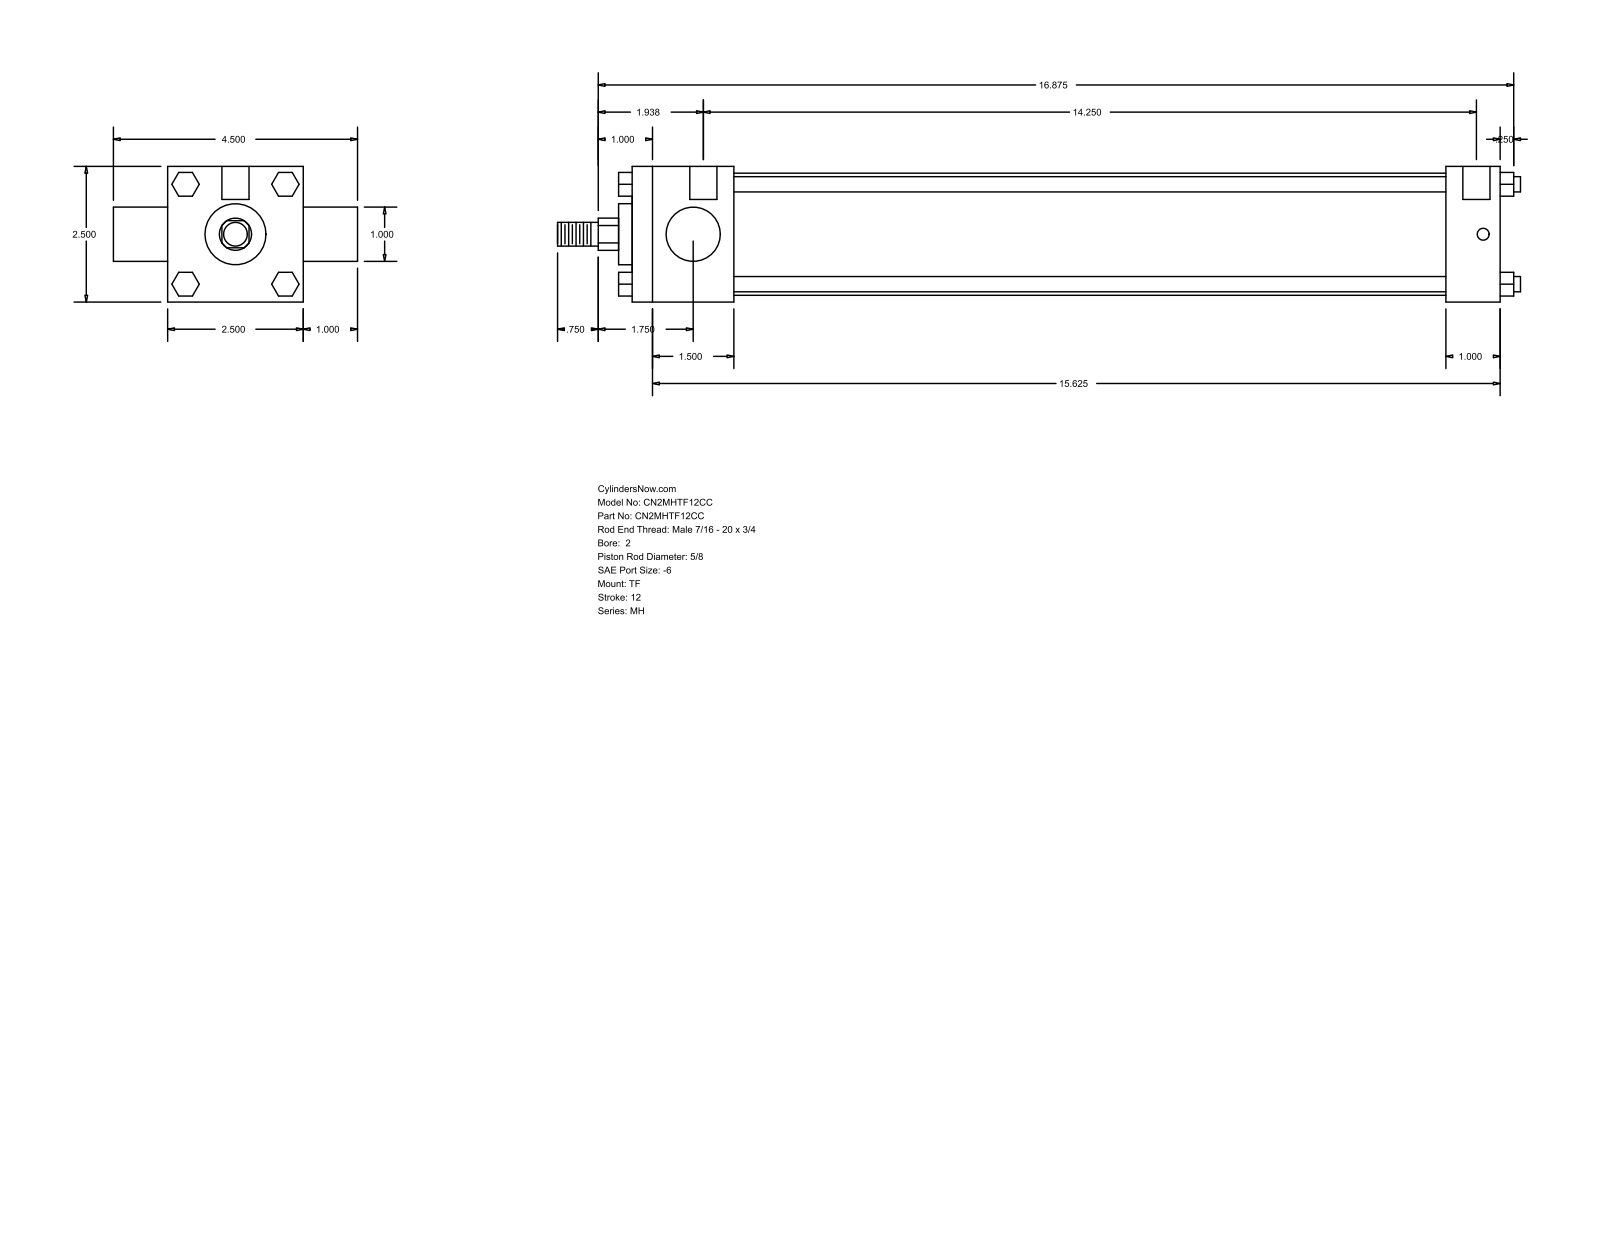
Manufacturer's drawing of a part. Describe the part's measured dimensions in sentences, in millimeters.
The part is named "MH_TF__0200_0.625". Its 3-D file was written by "GSSL Pune (CONFIG_CONTROL_DESIGN)". It is 0 solids with 120 faces: 92 planar, 28 cylindrical and 0 other. Overall it measures 450.85 by 114.3 by 63.5 millimeters. Round holes: 3 of diameter 5.56, 2 of diameter 12.7. Round bosses or shafts: 4 of diameter 7.14, 1 of diameter 57.15, 1 of diameter 28.57, 1 of diameter 25.4, 1 of diameter 15.88, 1 of diameter 11.11. Partial cylindrical surfaces (rounded edges, fillets, slot ends): 1 of radius 7.54. The main face-to-face distances are 63.5, 406.39, 47.62, 381, 333.38, 358.77, 25.39, 25.4, 6.35, 88.9. The hole center spacings are 3.18, 4.76, 361.95, 365.13, 366.71, 369.89.
